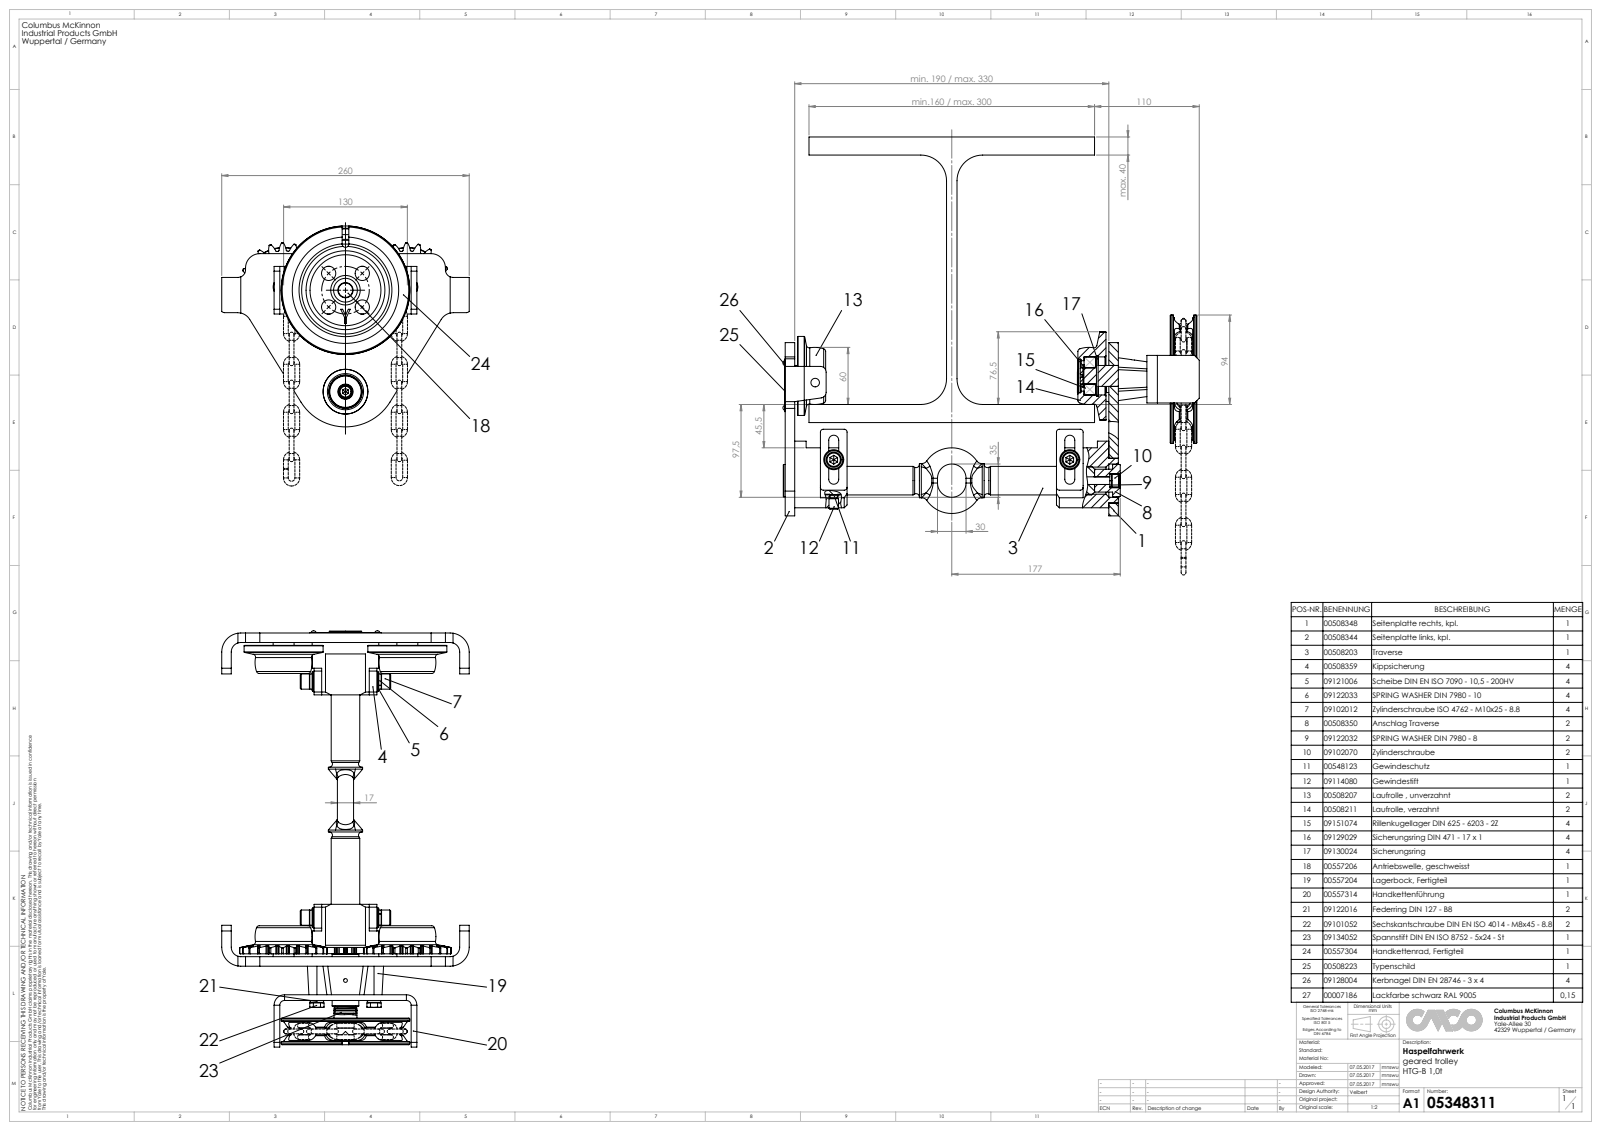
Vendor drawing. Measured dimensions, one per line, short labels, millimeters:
name: HTG-B 1,0t
written by: SolidWorks 2015 (AUTOMOTIVE_DESIGN)
unit: mm
bodies: 0 solids, 874 faces (276 planar, 360 cylindrical, 238 other)
size: 460.09 × 437.4 × 300
holes: 5× ⌀15, 2× ⌀2, 2× ⌀9, 2× ⌀22, 2× ⌀32, 2× ⌀34, 2× ⌀35.7, 1× ⌀4, 1× ⌀6, 1× ⌀35
bosses: 22× ⌀5, 2× ⌀83, 2× ⌀23.79, 2× ⌀21, 2× ⌀17, 2× ⌀16, 2× ⌀5.2, 1× ⌀135
rounds: 63× R20, 47× R1, 15× R10, 8× R1.5, 6× R3, 4× R5.25, 4× R6, 4× R15
face distances: 19, 281, 300, 262, 11, 10, 169.5, 180.5, 340, 159.5
hole spacings: 35.36, 21.55, 49.42, 50.01, 50.85, 51.81, 70.22, 83.9
